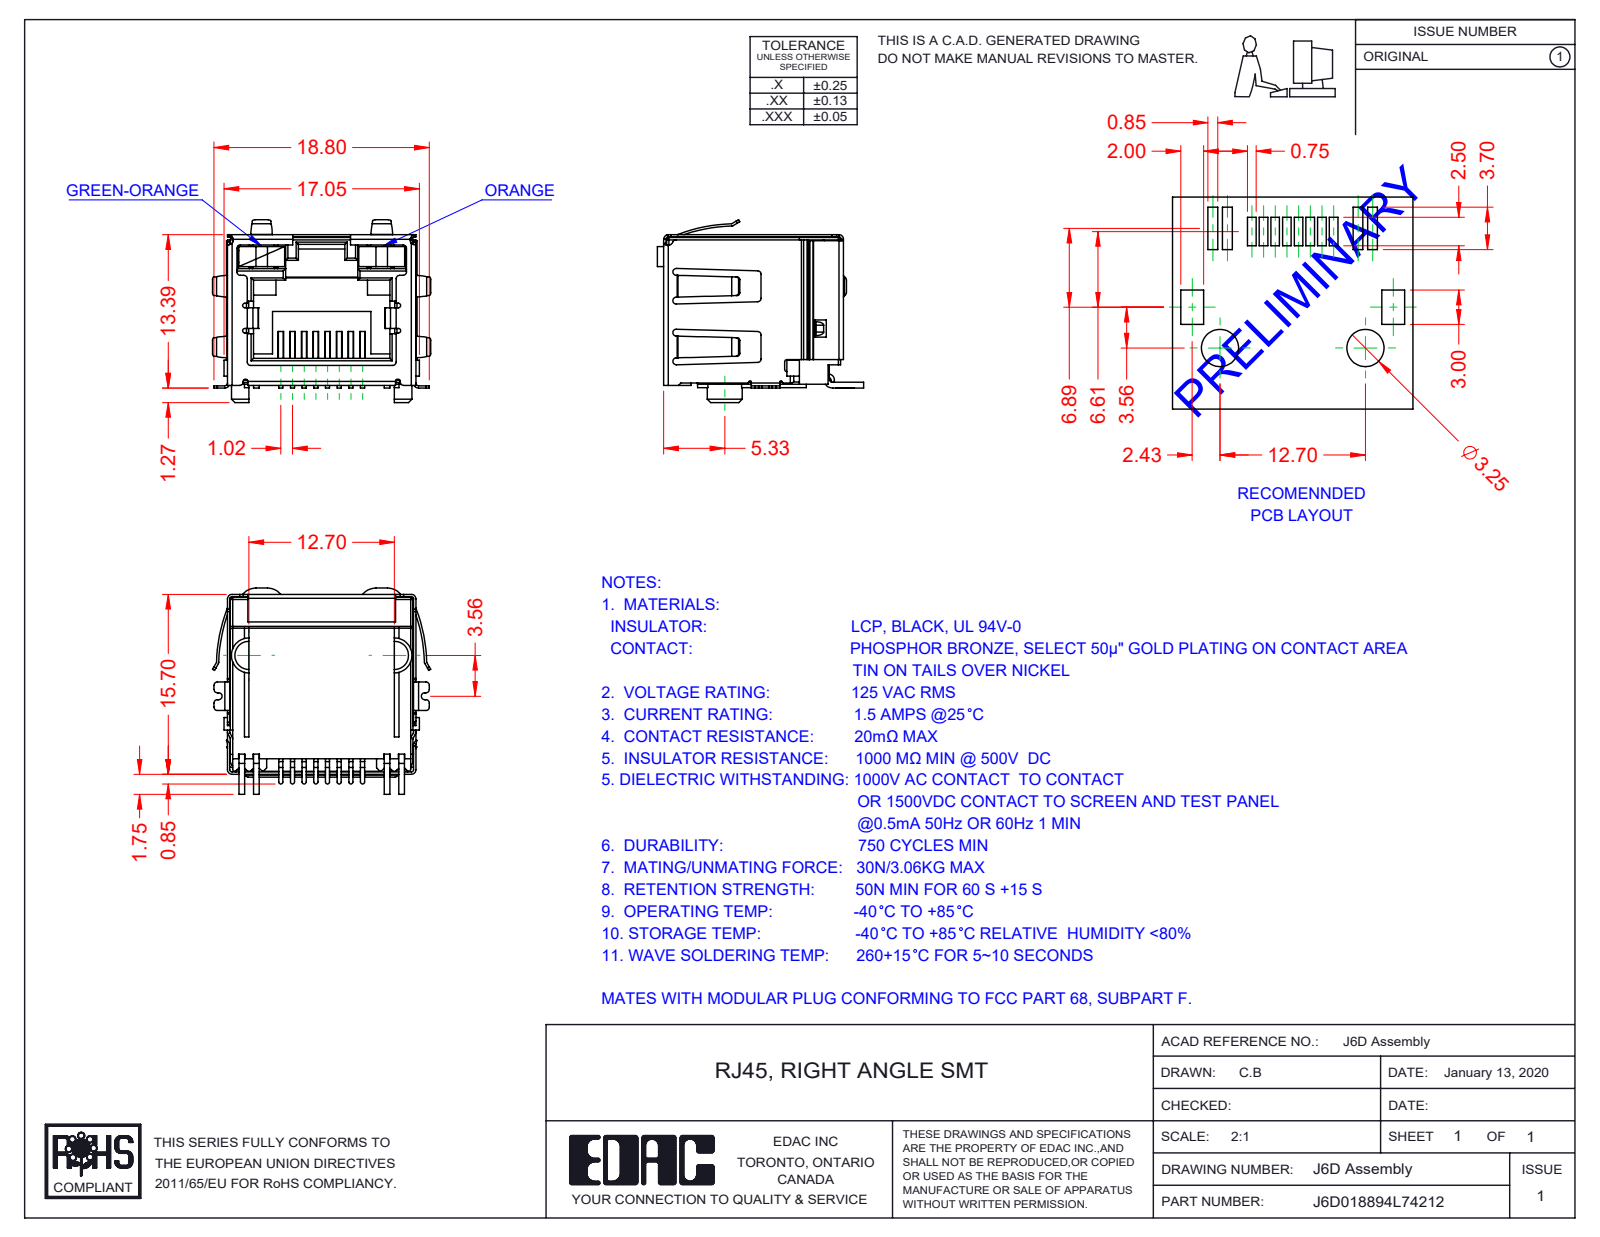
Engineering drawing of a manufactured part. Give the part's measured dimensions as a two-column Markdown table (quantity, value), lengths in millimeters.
| quantity | value |
| --- | --- |
| part name | 6D Shield_LED - EMI; J6D018894L74212; 6D LED LH_7-Green-Orange; 6D Insulator (+2 more) |
| STEP written by | SolidWorks 2016 (CONFIG_CONTROL_DESIGN) |
| units | millimeters |
| bodies | 12 solids, 1031 faces (702 planar, 284 cylindrical, 45 other) |
| overall size | 19.06 × 18 × 15.95 |
| volume | 1 790 mm³ |
| surface area | 4 796 mm² |
| partial cylindrical surfaces (radius × count) | 0.3 × 55, 0.2 × 40, 0.4 × 19, 0.25 × 16, 0.1 × 12, 0.15 × 8, 0.18 × 8, 0.5 × 6 |
| main face-to-face distances | 16, 16.2, 16.25, 2.25, 1, 15.95, 12.8, 0.45, 13.05, 10.6 |
